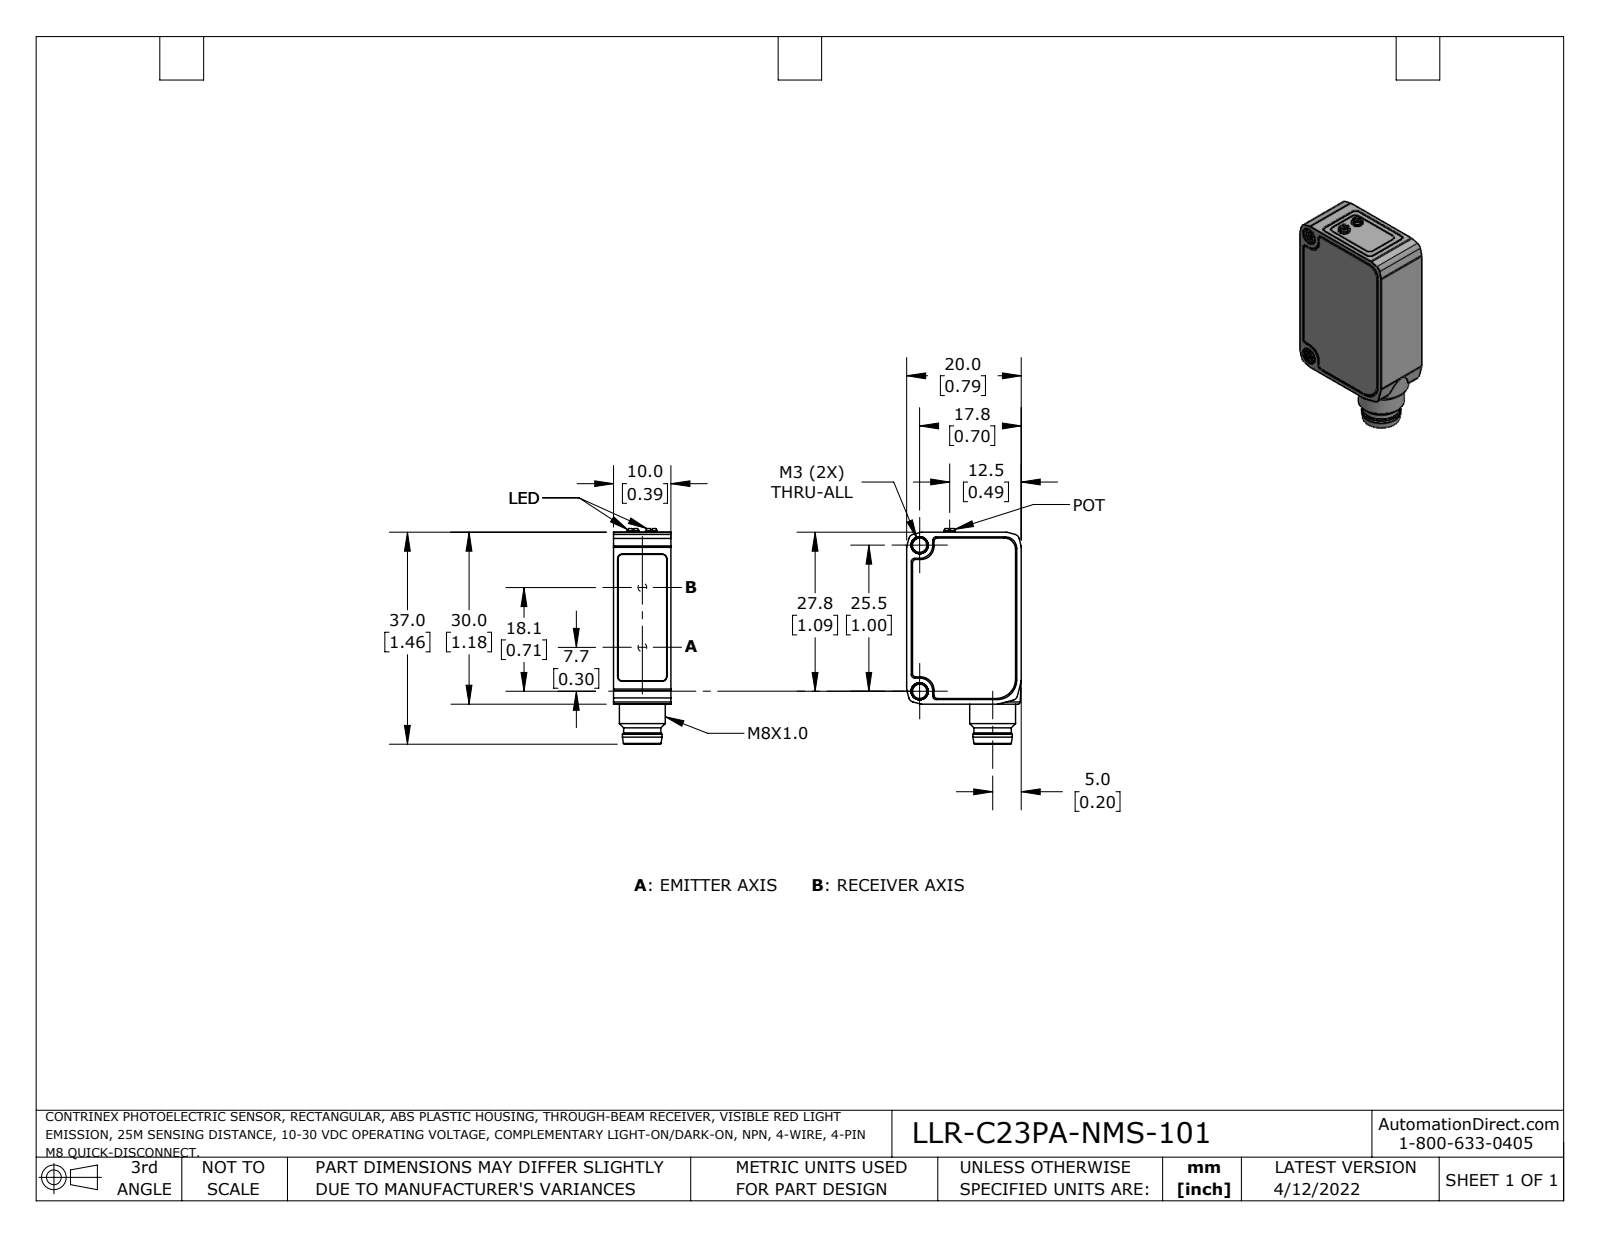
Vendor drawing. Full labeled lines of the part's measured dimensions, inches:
Part name (STEP PRODUCT): LLR-C23PA-NMS-101
STEP written by: SolidWorks 2021 (AUTOMOTIVE_DESIGN)
Units: inches
Bodies: 1 solid, 274 faces (87 planar, 136 cylindrical, 51 other)
Overall size (bounding box): 1.482 × 0.787 × 0.394
Volume: 0.363 in³ · Surface area: 4.36 in²
Round holes (diameter × count): ⌀0.098 ×2, ⌀0.142 ×2, ⌀0.228 ×1
Round bosses / shafts (diameter × count): ⌀0.039 ×4, ⌀0.079 ×2, ⌀0.315 ×1, ⌀0.272 ×1, ⌀0.256 ×1
Partial cylindrical surfaces — rounded edges, fillets, slot ends (radius × count): R0.031 ×20, R0.039 ×11, R0.024 ×8, R0.091 ×4, R0.079 ×2, R0.134 ×2
Main face-to-face distances: 0.394, 0.785, 1.177, 0.787, 1.181, 0.028, 1.179, 0.03, 0.031, 0.039
Hole centre spacings: 1.004
